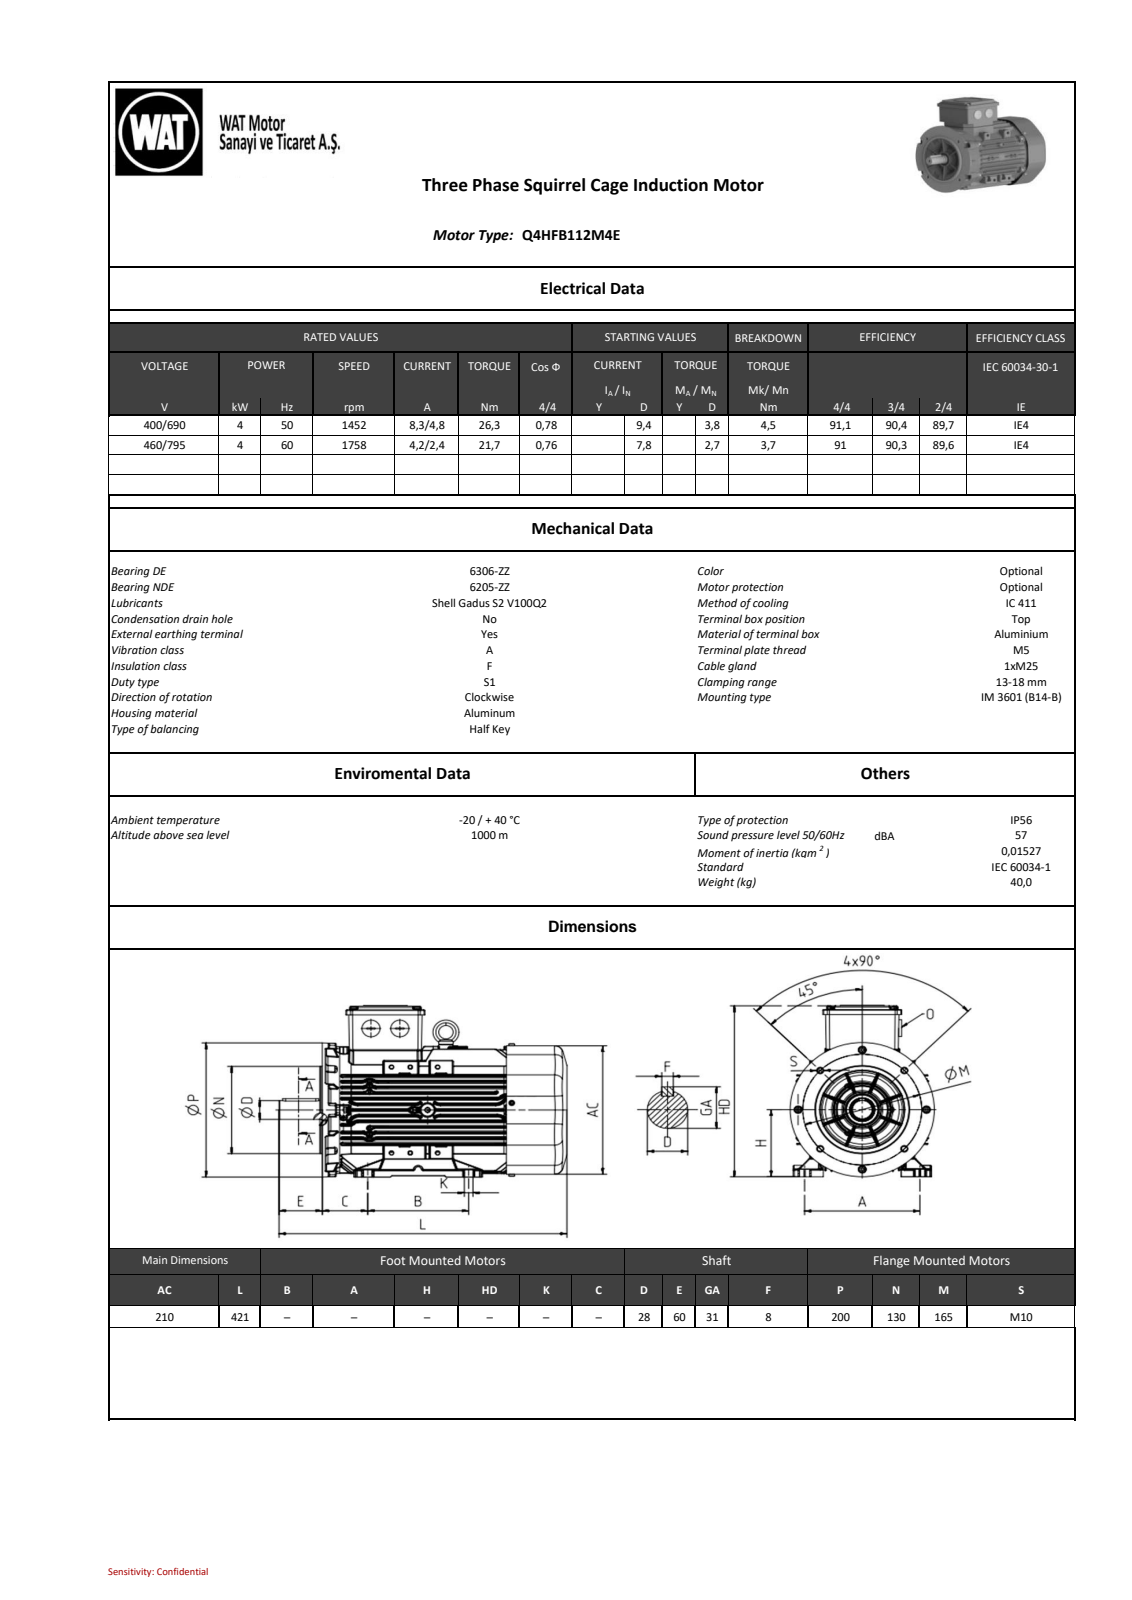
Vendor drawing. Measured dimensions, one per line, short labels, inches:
name: QH series_ 112_B14b _DEEP COVER__stp_objects
written by: SIEMENS PLM Software NX2206.8101 (AUTOMOTIVE_DESIGN)
unit: in
bodies: 0 solids, 6724 faces (1503 planar, 2599 cylindrical, 2622 other)
size: 16.575 × 10.531 × 8.622
holes: 2× ⌀0.181, 1× ⌀0.138, 1× ⌀0.315, 1× ⌀0.335, 1× ⌀1.85, 1× ⌀3.071
bosses: 7× ⌀0.315, 2× ⌀0.984, 1× ⌀7.402, 1× ⌀5.118, 1× ⌀1.411, 1× ⌀1.181, 1× ⌀1.161, 1× ⌀1.15
rounds: 658× R0.079, 607× R0.031, 349× R0.02, 279× R0.039, 64× R0.118, 10× R0.157, 5× R0.197, 4× R0.03
face distances: 0.039, 0.433, 0.846, 1.416, 3.919, 3.56, 0.983, 2.714, 0.321, 4.444
